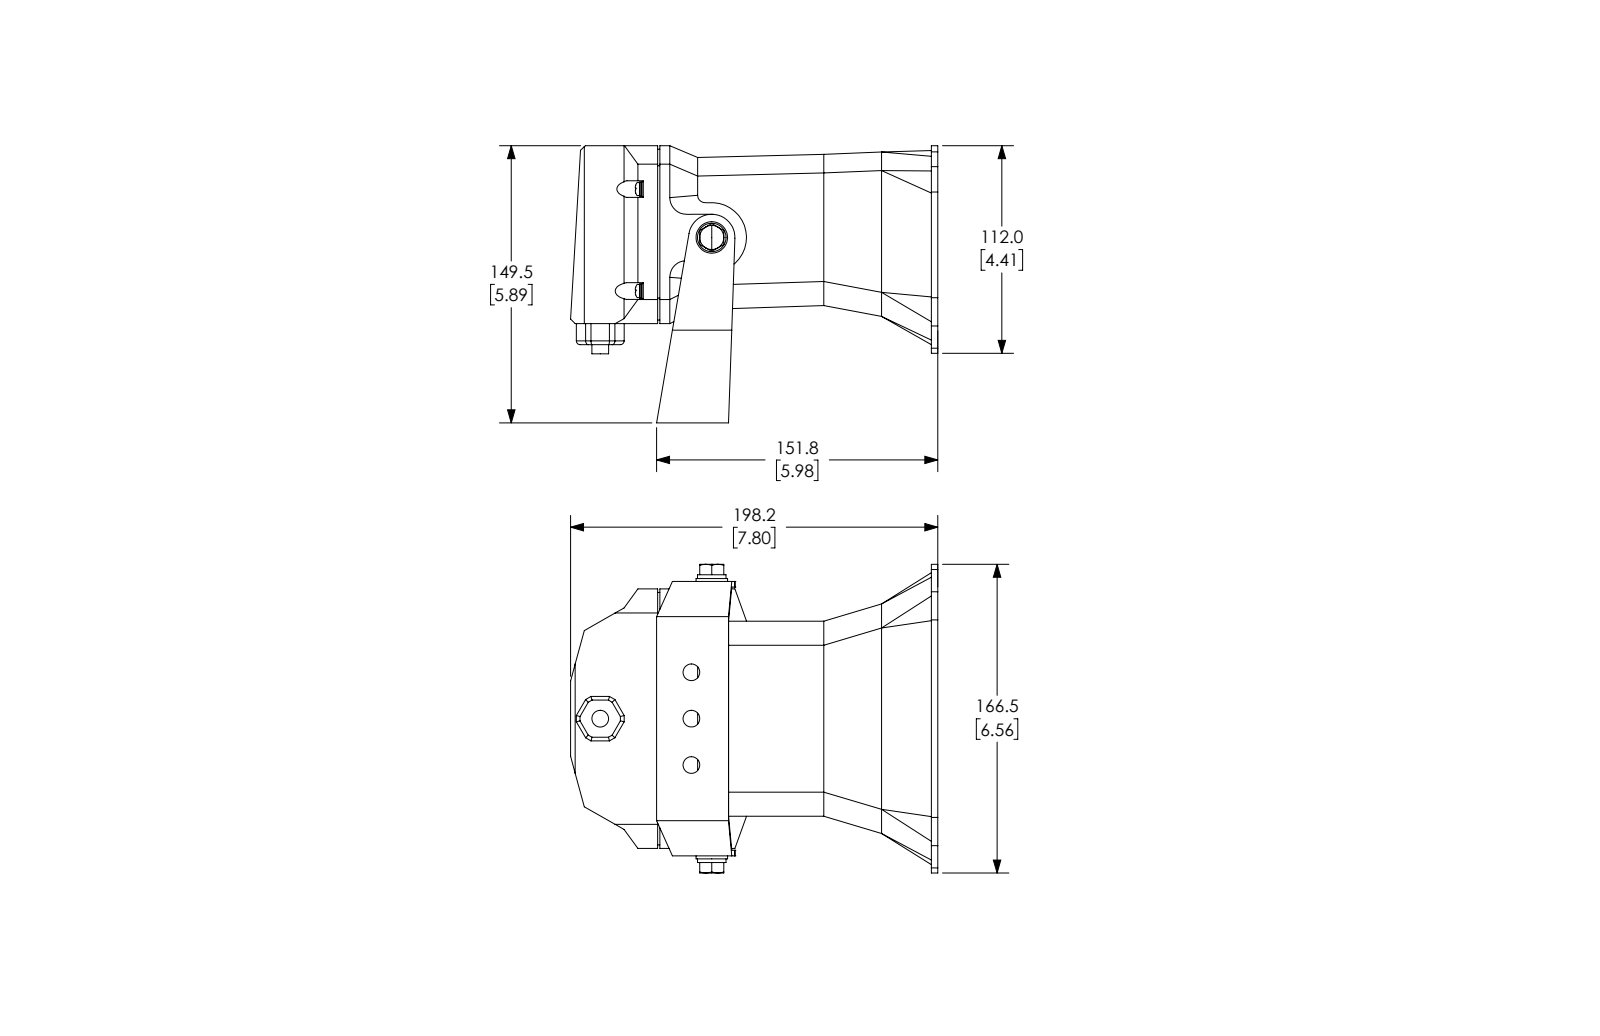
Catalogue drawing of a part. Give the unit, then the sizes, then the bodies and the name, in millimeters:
Units: millimetres
Overall size (bounding box): 198.2 × 166.5 × 149.5
Round holes (diameter × count): ⌀9 ×3, ⌀8 ×1, ⌀76.5 ×1
Round bosses / shafts (diameter × count): ⌀8 ×4, ⌀7.6 ×4, ⌀17 ×1, ⌀15.4 ×1, ⌀9 ×1
Partial cylindrical surfaces — rounded edges, fillets, slot ends (radius × count): R2 ×12, R12.5 ×1
Main face-to-face distances: 3, 96, 146.5, 53.5, 149.5, 50.5, 17.4, 122.6, 145, 105.2
Hole centre spacings: 25, 50
Volume: 1 618 000 mm³ · Surface area: 176 100 mm²
Bodies: 2 solids, 306 faces (158 planar, 59 cylindrical, 89 other)
Part name (STEP PRODUCT): EHS-M1TE
STEP written by: SolidWorks 2018 (AUTOMOTIVE_DESIGN)
